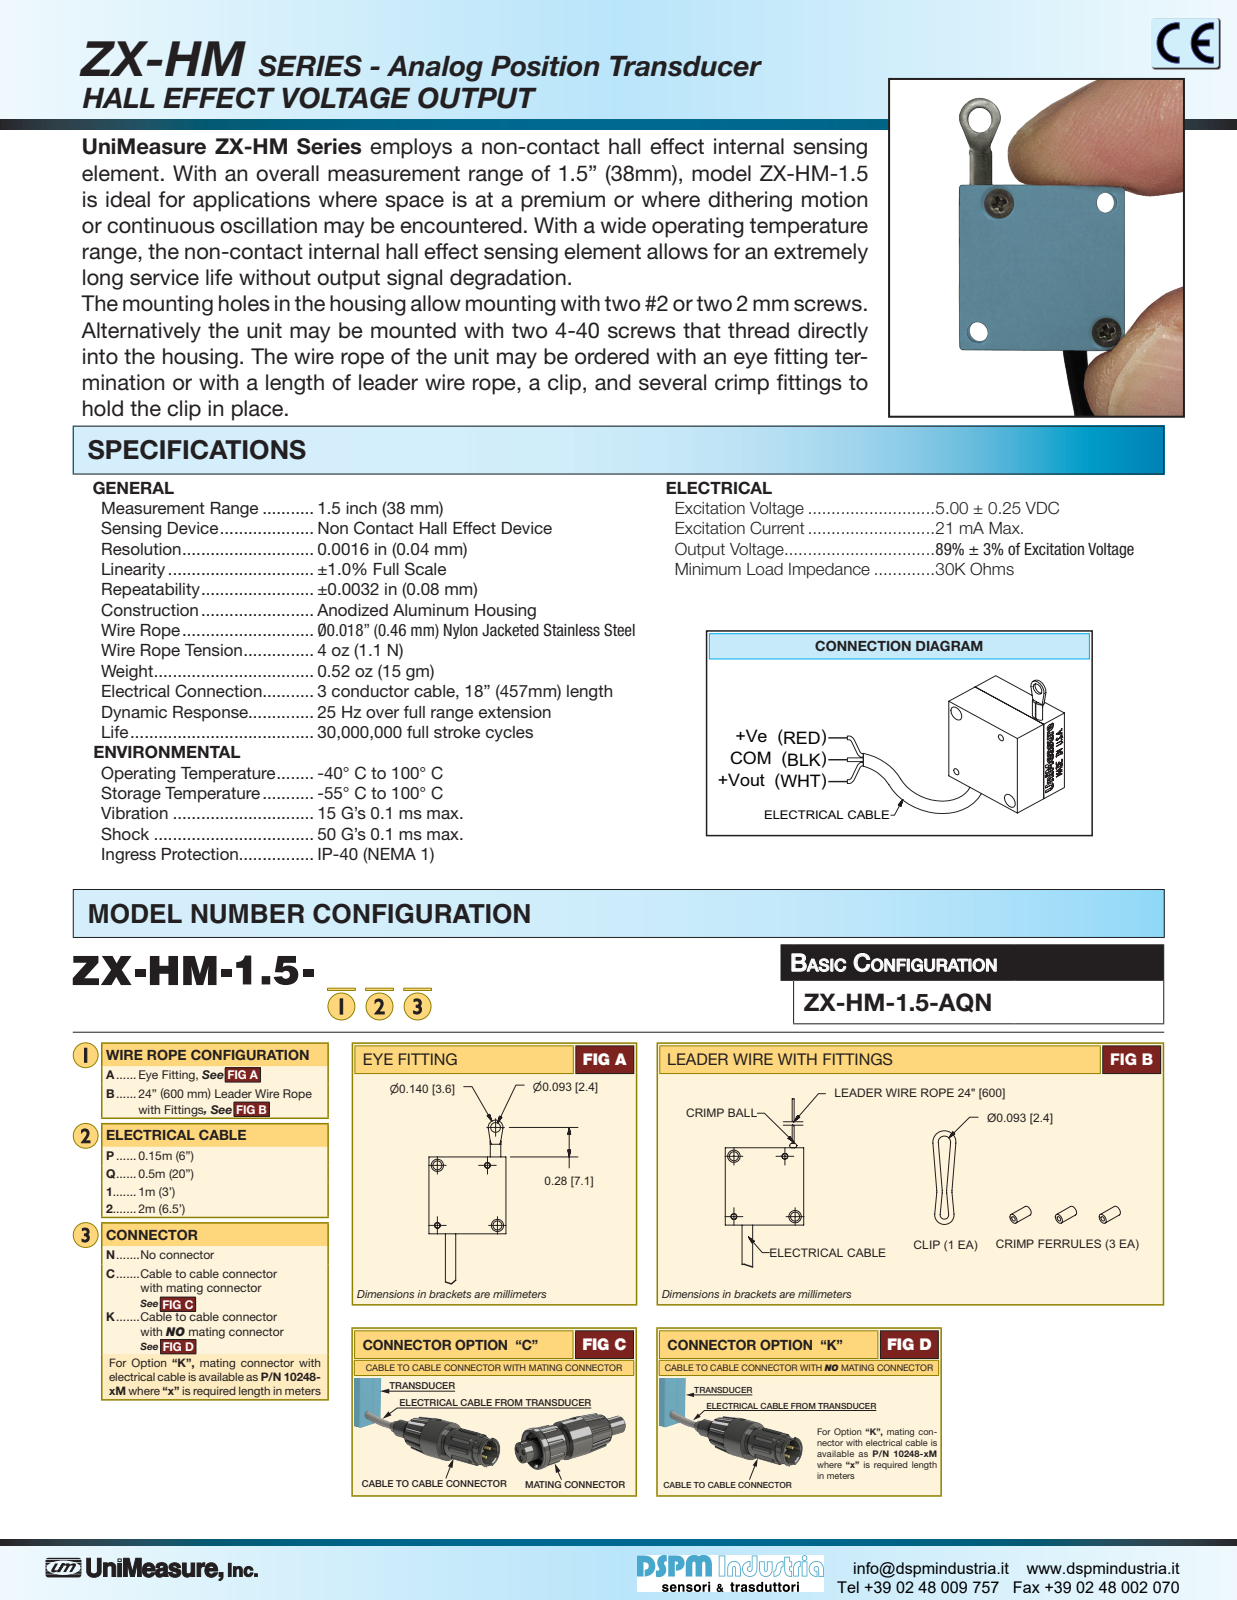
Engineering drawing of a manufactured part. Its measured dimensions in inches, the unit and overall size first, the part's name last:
Units: inches
Overall size (bounding box): 1.505 × 0.73 × 0.502
Round holes (diameter × count): ⌀0.056 ×2, ⌀0.076 ×2, ⌀0.085 ×2, ⌀0.116 ×2, ⌀0.029 ×1, ⌀0.058 ×1, ⌀0.093 ×1, ⌀0.1 ×1, ⌀0.595 ×1
Round bosses / shafts (diameter × count): ⌀0.123 ×2, ⌀0.073 ×2, ⌀0.115 ×1
Partial cylindrical surfaces — rounded edges, fillets, slot ends (radius × count): R0.012 ×8, R0.109 ×8, R0.031 ×5, R0.022 ×1, R0.07 ×1, R0.319 ×1, R0.381 ×1
Main face-to-face distances: 0.73, 0.5, 0.115, 0.615, 0.062, 0.438, 0.475, 0.413, 0.025, 0.22
Hole centre spacings: 0.403, 0.57, 0.343, 0.368, 0.475, 0.483, 0.578, 0.659
Volume: 0.154 in³ · Surface area: 4.858 in²
Bodies: 2 solids, 463 faces (315 planar, 46 cylindrical, 102 other)
Part name (STEP PRODUCT): ZX-HM Shell
STEP written by: Autodesk Inventor 2011 (AUTOMOTIVE_DESIGN)
